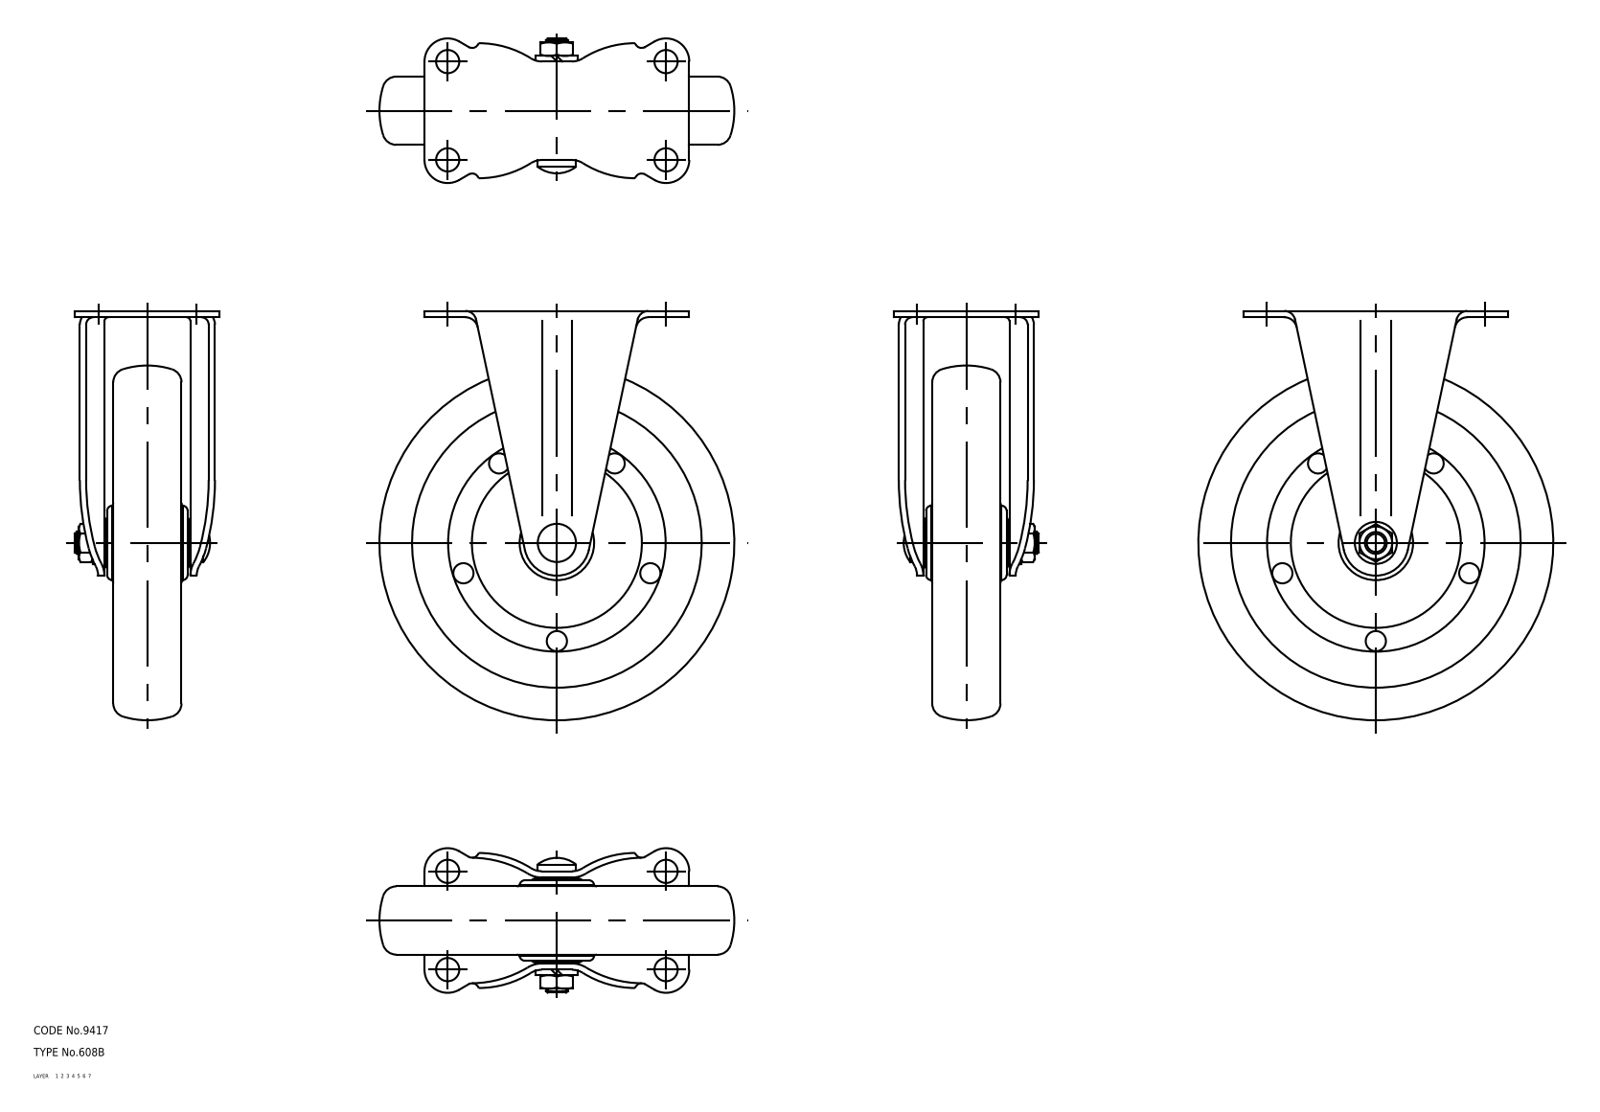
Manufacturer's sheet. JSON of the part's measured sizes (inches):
{"part_name": "67122727; 67122740; 67122753", "step_written_by": "CADfix (AUTOMOTIVE_DESIGN)", "units": "inches", "bodies": {"solids": 3, "faces": 198, "planar": 0, "cylindrical": 0, "other": 198}, "overall_size": [5.906, 5.118, 2.087], "volume_in3": 18.67, "surface_area_in2": 98.55}
